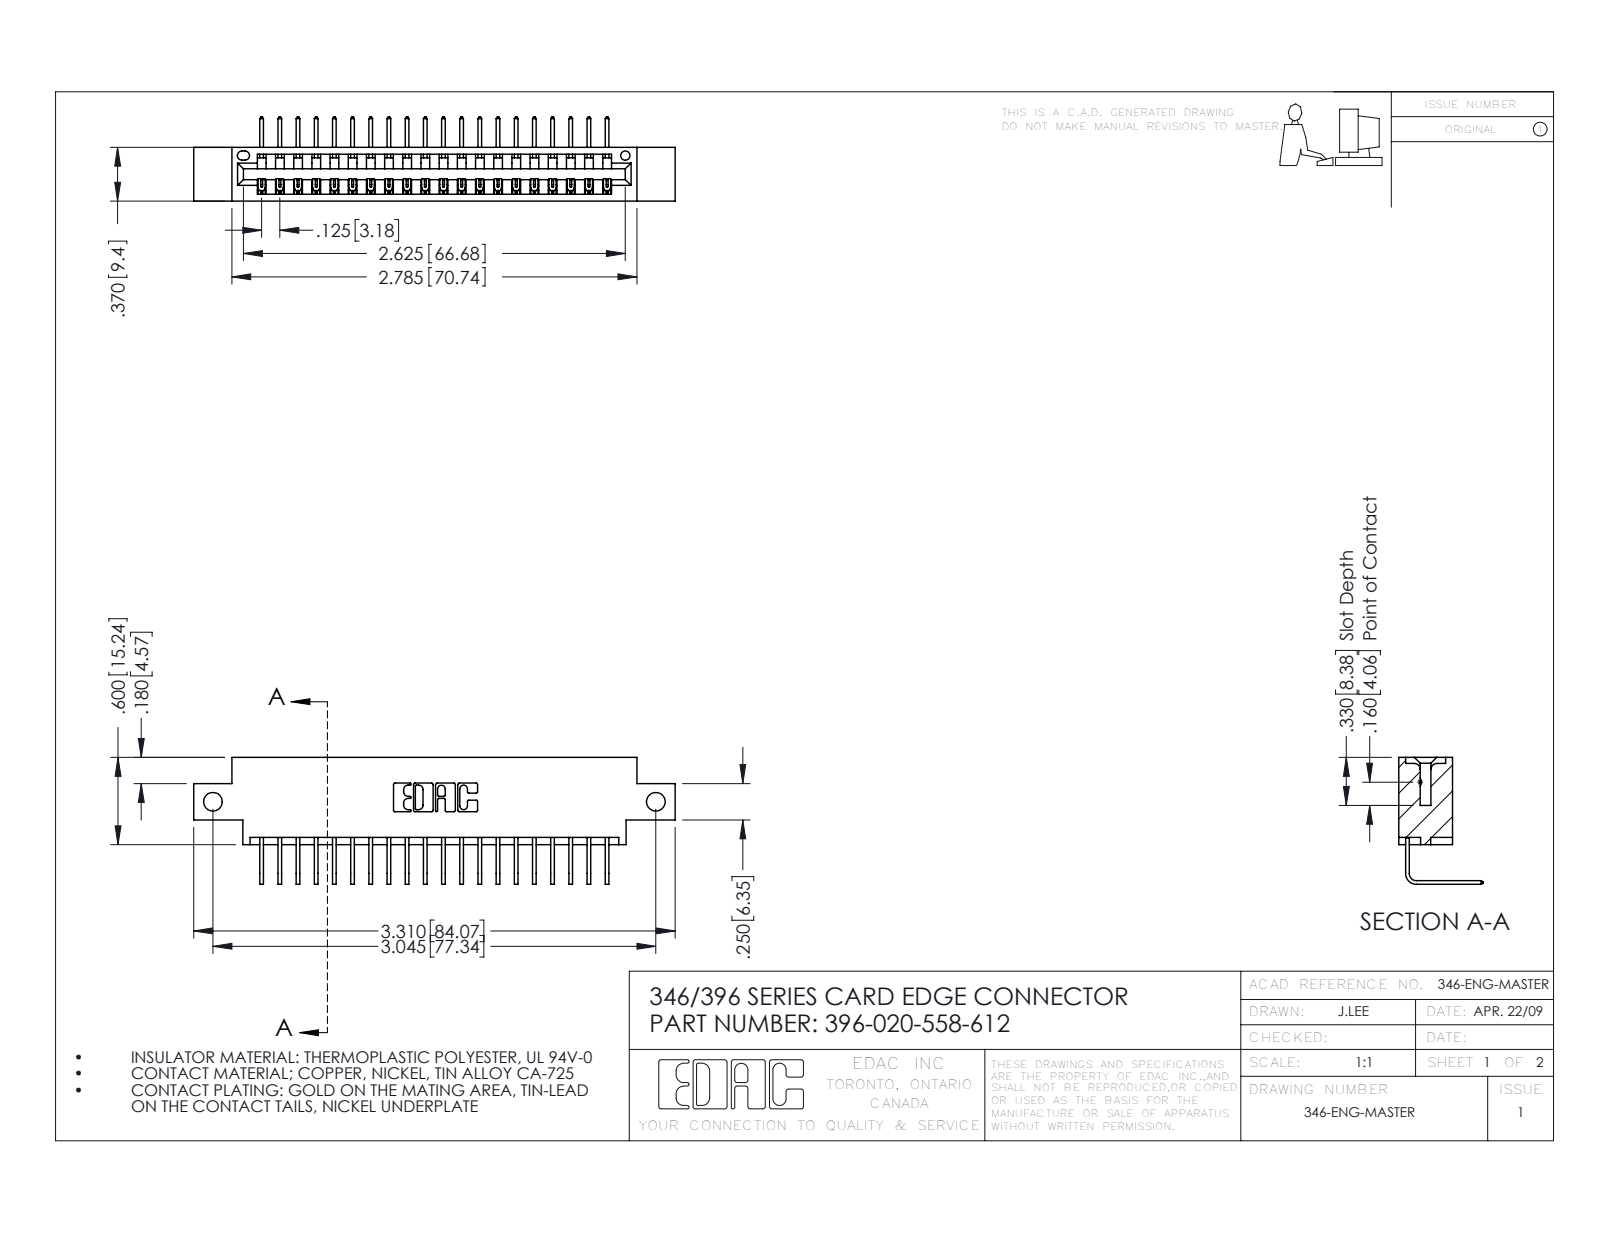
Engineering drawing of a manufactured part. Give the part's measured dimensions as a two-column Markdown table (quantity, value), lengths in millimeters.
| quantity | value |
| --- | --- |
| part name | 346 Part_0.170 Offset - Side Mount; 396-020-558-612; 345-292-001_558 Tail - 2 |
| STEP written by | SolidWorks 2016 (CONFIG_CONTROL_DESIGN) |
| units | millimeters |
| bodies | 21 solids, 1326 faces (920 planar, 406 cylindrical, 0 other) |
| overall size | 84.1 × 22.2 × 14.7 |
| volume | 7 720 mm³ |
| surface area | 9 826 mm² |
| round holes (diameter × count) | 3.3 × 2, 1.6 × 1 |
| partial cylindrical surfaces (radius × count) | 0.2 × 40, 0.3 × 22, 0.2 × 6, 0.8 × 6, 0.7 × 3, 0.8 × 2, 1 × 2, 0.4 × 1 |
| main face-to-face distances | 8.2, 1.2, 9.4, 6.4, 7.6, 0.6, 1.8, 3.8, 5.6, 2.5 |
| hole center spacings | 77.3 |
